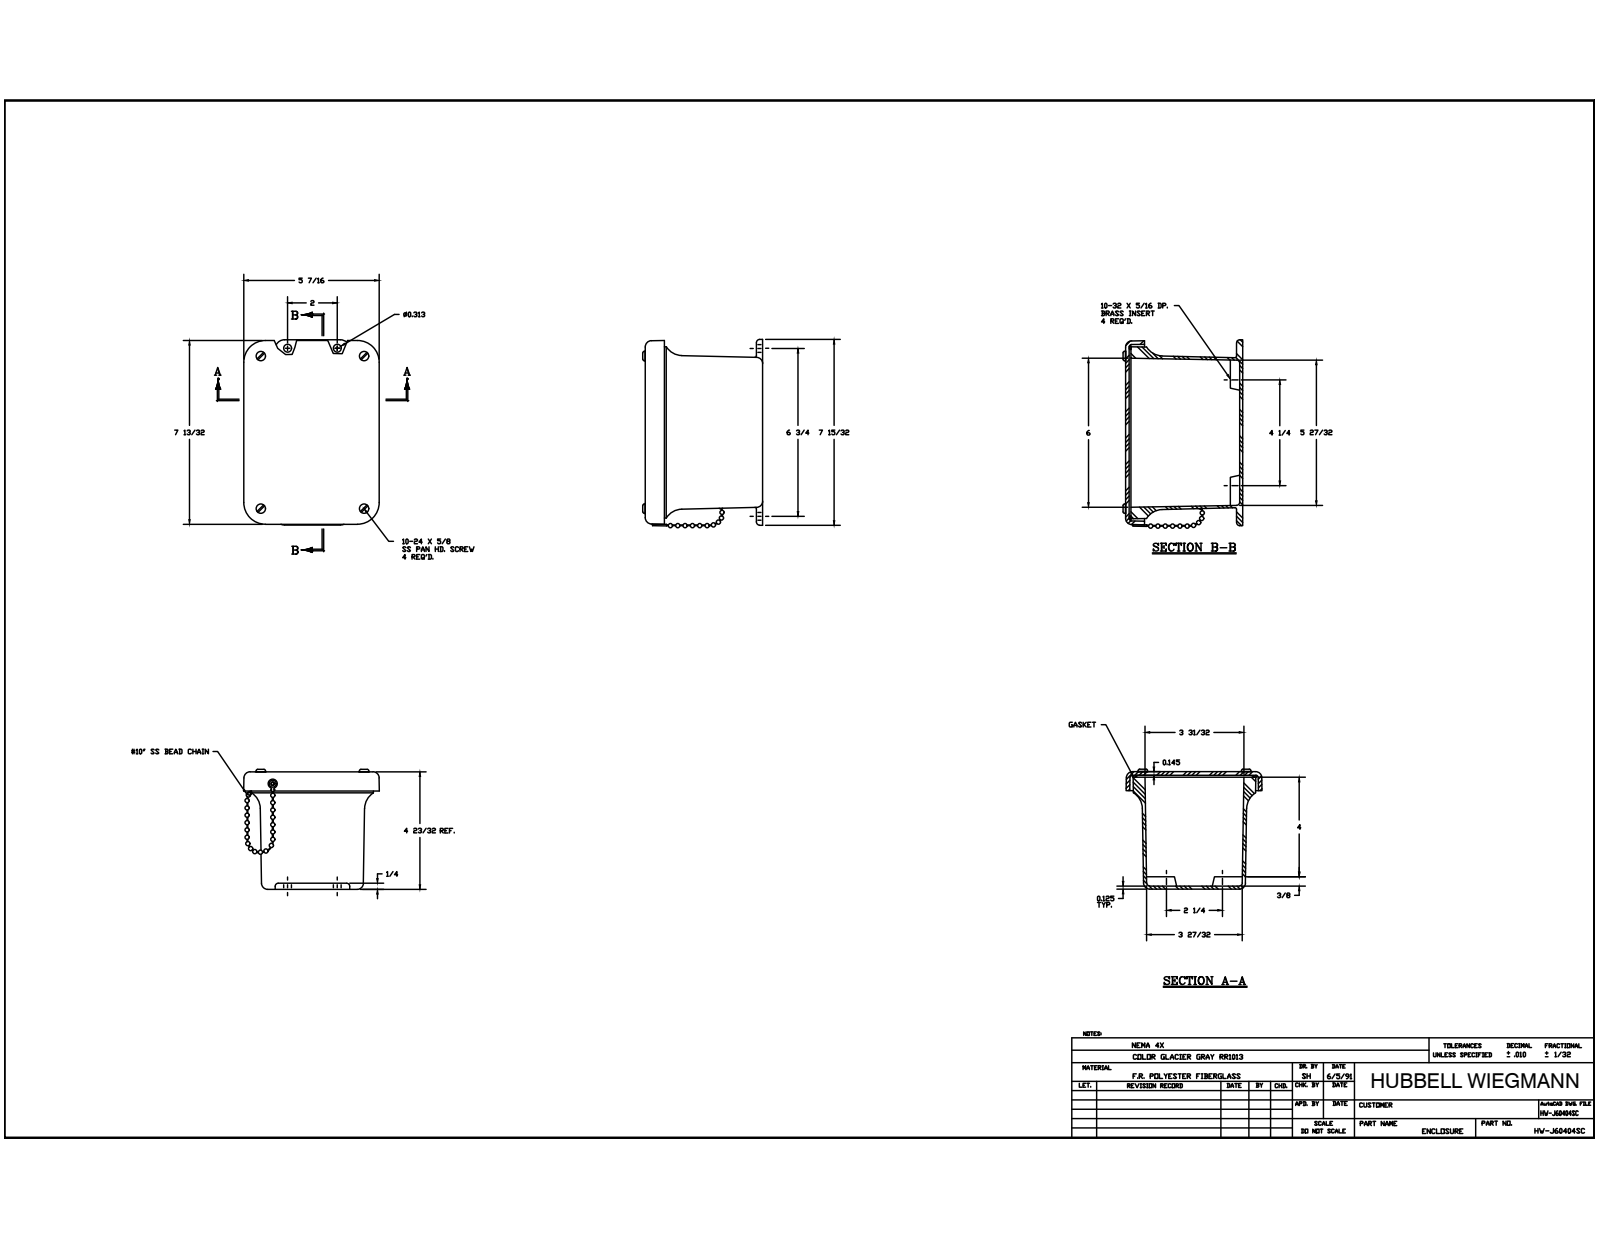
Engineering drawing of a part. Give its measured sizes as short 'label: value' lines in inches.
name: J604W_1; RMINS45821P_1; RMINS45821P_2; RMINS45821P_3 (+8 more)
written by: Autodesk Inventor 2014 (AUTOMOTIVE_DESIGN)
unit: in
bodies: 21 solids, 862 faces (185 planar, 285 cylindrical, 392 other)
size: 8.064 × 5.808 × 4.835
volume: 31.18 in³; area: 383.5 in²
holes: 5× ⌀0.152, 4× ⌀0.145, 4× ⌀0.156, 4× ⌀0.218, 3× ⌀0.14, 2× ⌀0.187, 1× ⌀0.126
bosses: 8× ⌀0.27, 4× ⌀0.19, 4× ⌀0.156, 2× ⌀0.375, 2× ⌀0.25, 2× ⌀0.125, 1× ⌀0.283
rounds: 20× R0.031, 12× R0.125, 8× R0.2, 8× R0.25, 4× R0.375, 4× R0.75, 2× R0.01, 2× R0.063
face distances: 0.145, 4.559, 4.704, 0.125, 4.434, 4.579, 4.5, 4.375, 0.059, 0.204
hole spacings: 3.339, 1.341, 2.25, 4.156, 4.25, 4.808, 5.28, 6.102
